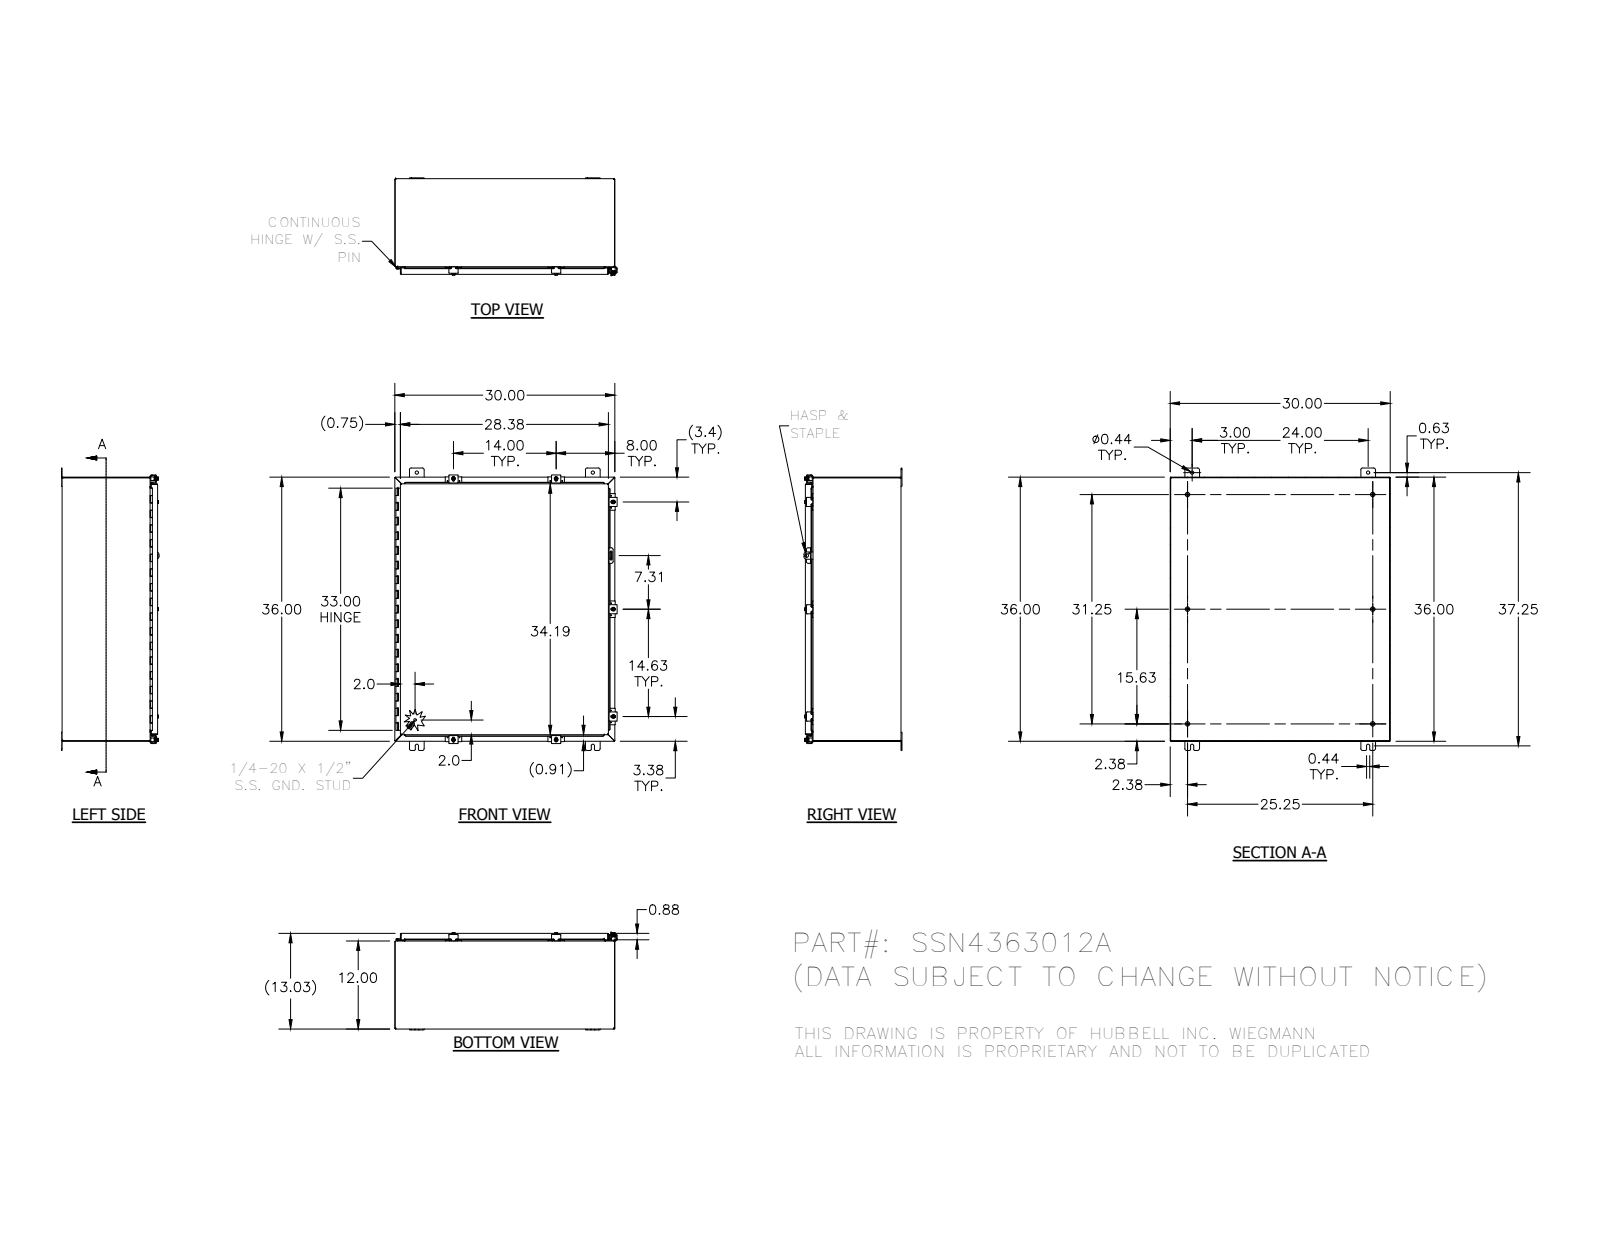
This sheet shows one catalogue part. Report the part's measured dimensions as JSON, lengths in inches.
{"part_name": "38859; 30824-1; 32912; 34871 (+8 more)", "step_written_by": "SolidWorks 2014 (AUTOMOTIVE_DESIGN)", "units": "inches", "bodies": {"solids": 54, "faces": 2180, "planar": 862, "cylindrical": 947, "other": 371}, "overall_size": [38.5, 30.216, 13.355], "volume_in3": 321.8, "surface_area_in2": 8513, "round_holes": [[0.11, 14], [0.211, 7], [0.281, 7], [0.3, 7], [0.438, 4], [0.125, 1], [0.156, 1], [0.5, 1]], "round_bosses_or_shafts": [[0.25, 9], [0.52, 7], [0.5, 7], [0.35, 7], [0.625, 6], [0.33, 6], [0.337, 1], [0.12, 1]], "partial_cylinders_radius": [[0.03, 83], [0.125, 37], [0.25, 33], [0.031, 23], [0.105, 23], [0.062, 18], [0.141, 14], [0.1, 10]], "face_to_face_distances": [0.074, 12.959, 12.885, 13.033, 29.926, 35.926, 30, 29.852, 36, 35.852], "hole_center_spacings": [0.876, 35.298, 14, 1.625, 13.191, 14.816, 34.961, 34.998]}
